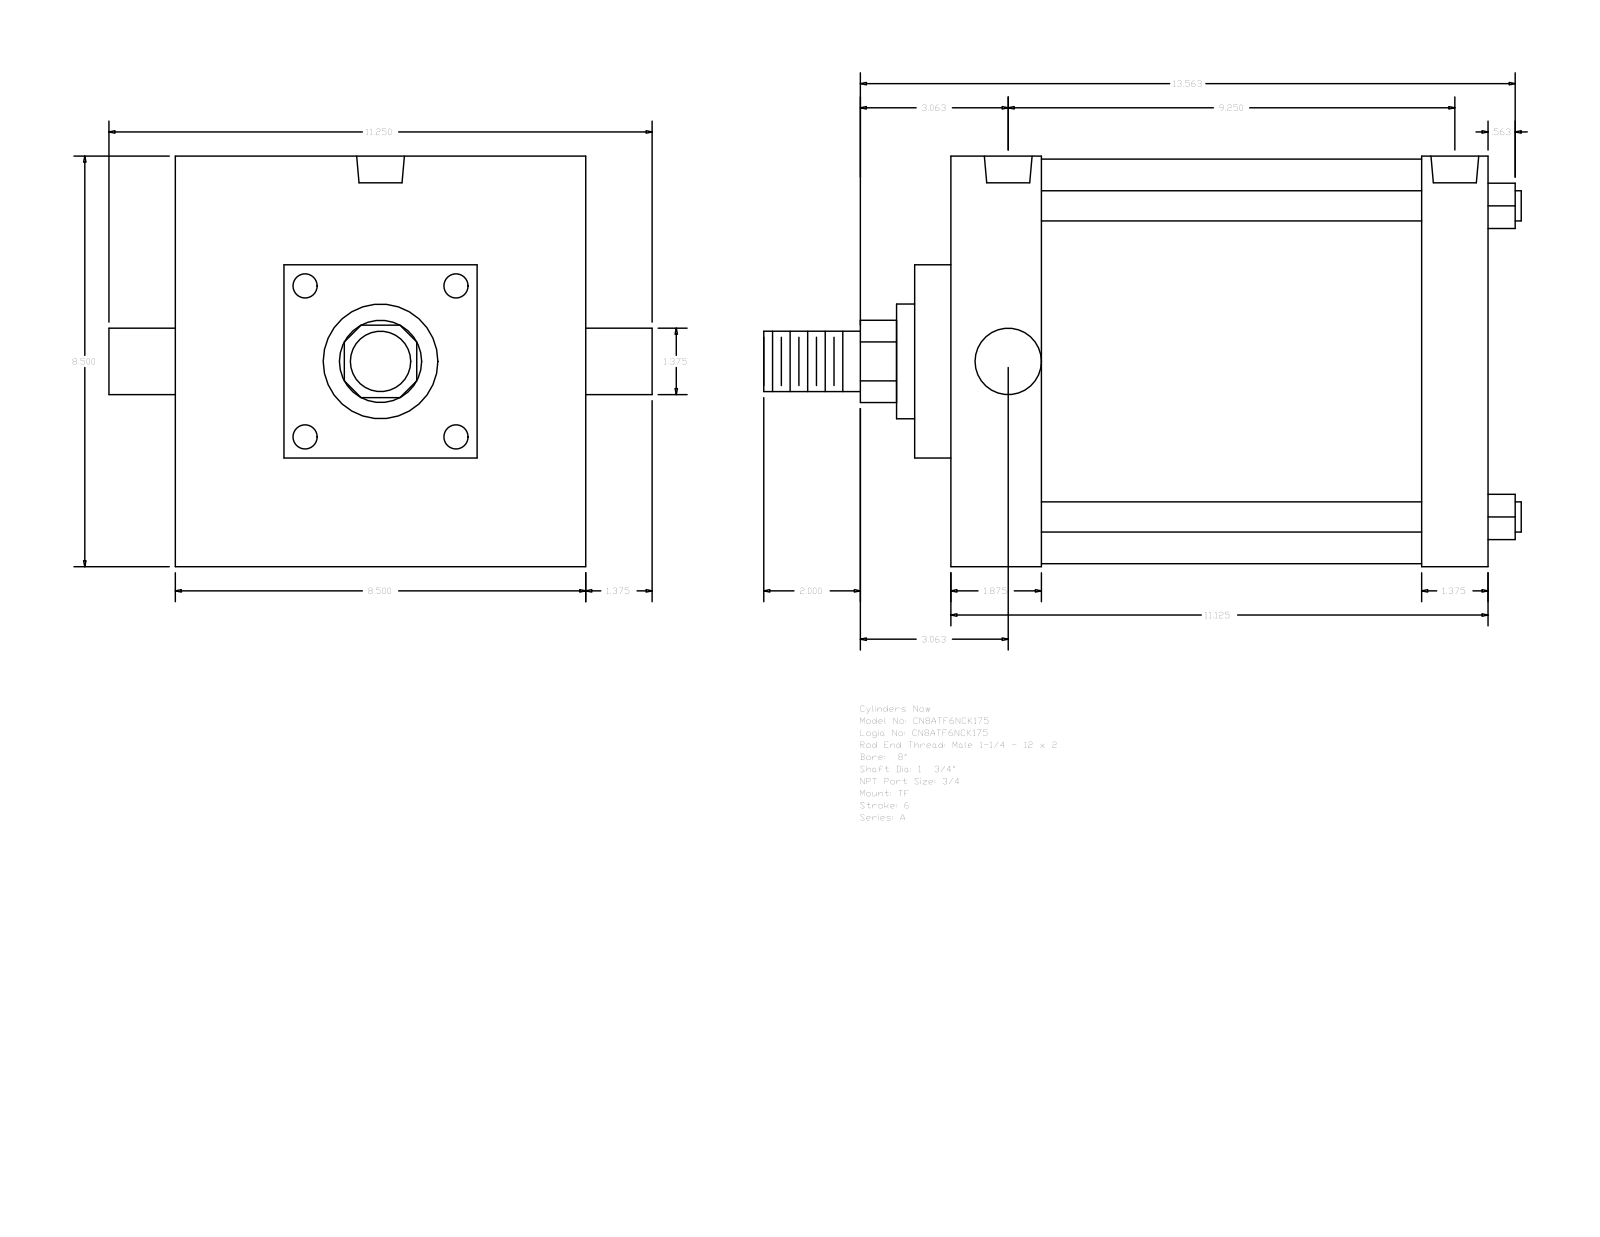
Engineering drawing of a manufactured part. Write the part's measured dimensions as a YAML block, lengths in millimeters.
part_name: "A_TF__0800_1.75"
step_written_by: "GSSL Pune (CONFIG_CONTROL_DESIGN)"
units: millimeters
bodies: {solids: 0, faces: 89, planar: 65, cylindrical: 24, other: 0}
overall_size: [398.46, 285.75, 215.9]
round_holes:
  - {diameter: 15.08, count: 3}
  - {diameter: 25.12, count: 2}
round_bosses_or_shafts:
  - {diameter: 15.88, count: 4}
  - {diameter: 212.72, count: 1}
  - {diameter: 60.33, count: 1}
  - {diameter: 44.45, count: 1}
  - {diameter: 34.92, count: 1}
  - {diameter: 31.75, count: 1}
partial_cylinders:
  - {radius: 21.63, count: 1}
face_to_face_distances: [282.58, 215.9, 34.93, 47.63, 234.95, 247.65, 200.02, 19.05, 57.15, 158.75]
hole_center_spacings: [6.35, 228.6, 222.25, 234.95]
